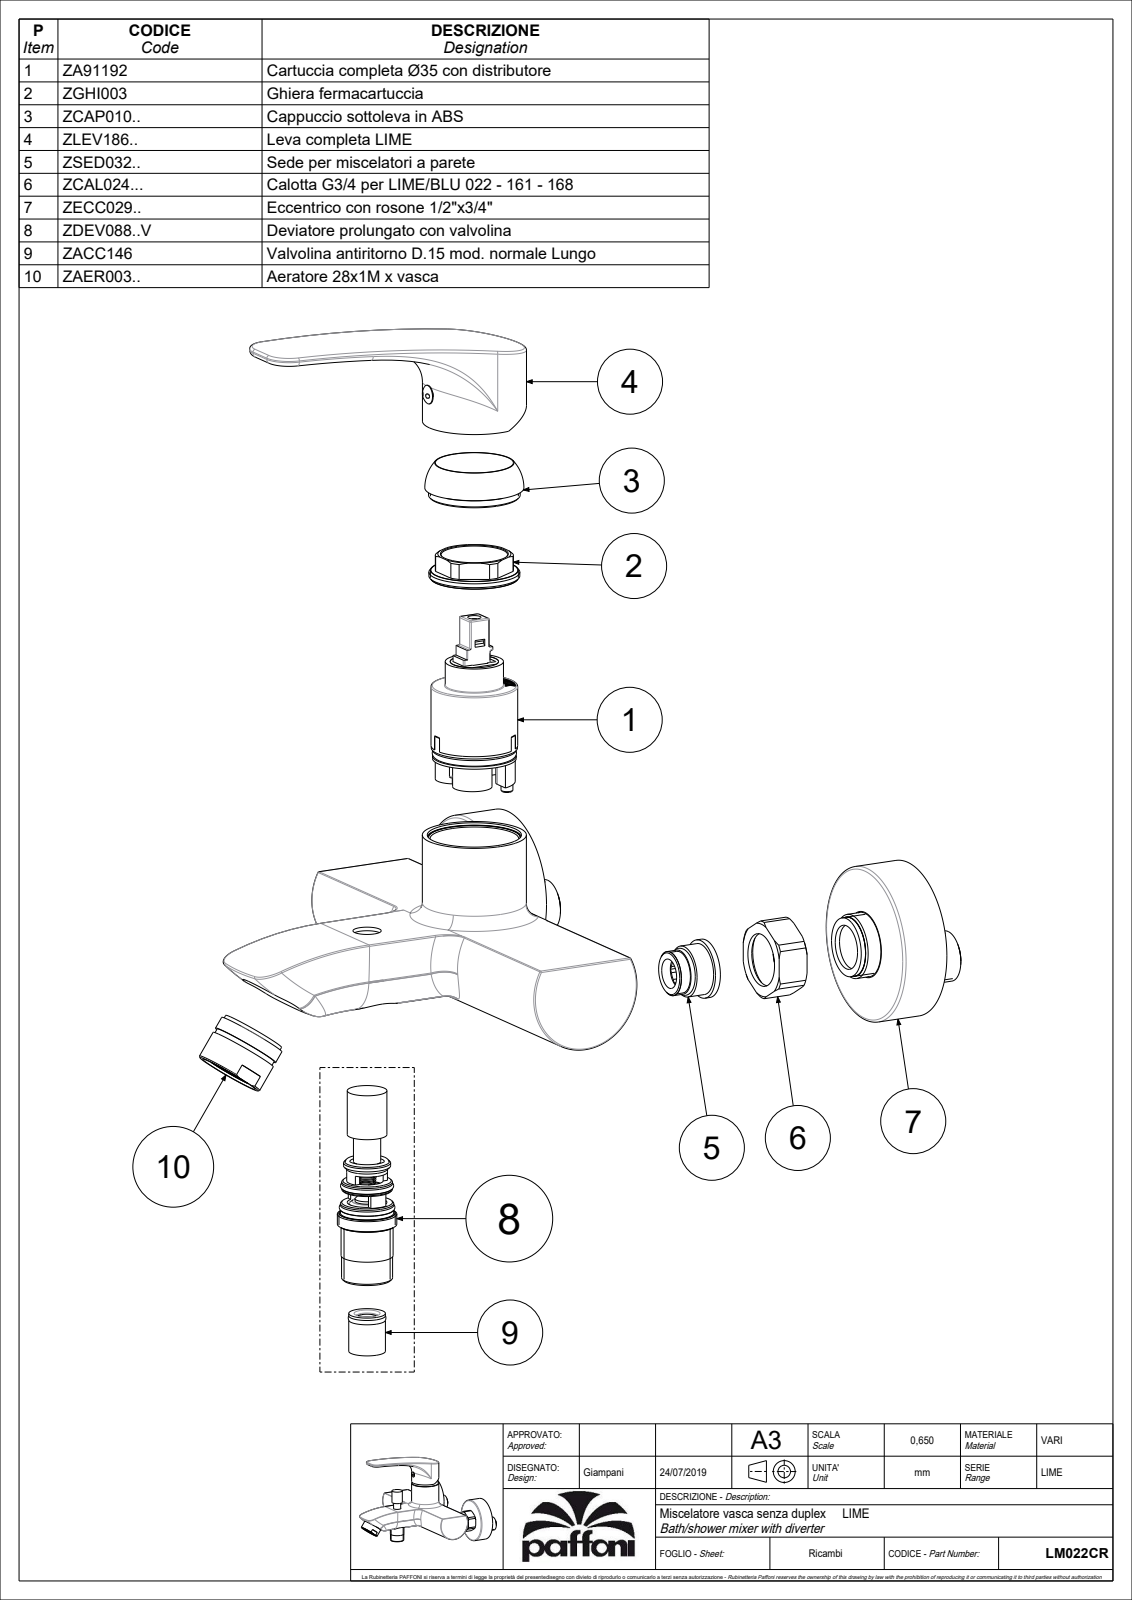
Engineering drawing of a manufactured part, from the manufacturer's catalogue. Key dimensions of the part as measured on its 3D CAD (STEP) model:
Part name (STEP PRODUCT): LM022CR
STEP written by: CREO PARAMETRIC BY PTC INC, 2020044 (CONFIG_CONTROL_DESIGN)
Units: millimetres
Bodies: 8 solids, 2855 faces (1983 planar, 443 cylindrical, 429 other)
Overall size (bounding box): 213.5 × 169.8 × 129.33
Volume: 216 308 mm³ · Surface area: 175 370 mm²
Round holes (diameter × count): ⌀12 ×6, ⌀25 ×4, ⌀9 ×3, ⌀7 ×2, ⌀8 ×2, ⌀16.3 ×2, ⌀18 ×2, ⌀19 ×2, ⌀21.5 ×2, ⌀24.1 ×2, ⌀62.3 ×2, ⌀3 ×1
Round bosses / shafts (diameter × count): ⌀24 ×3, ⌀20.8 ×3, ⌀63.5 ×2, ⌀42 ×2, ⌀28 ×2, ⌀27 ×2, ⌀23.8 ×2, ⌀10 ×2
Partial cylindrical surfaces — rounded edges, fillets, slot ends (radius × count): R0.5 ×66, R0.3 ×20, R1 ×18, R7.25 ×3, R0.2 ×2, R1.2 ×2, R4.5 ×2, R5.25 ×2
Main face-to-face distances: 2.5, 0.6, 88.75, 110, 67.5, 177.5, 65, 2, 21.25, 9.1
Hole centre spacings: 0.71, 8.51, 8.6, 13.04, 13.21, 13.51, 44.97, 45.54
